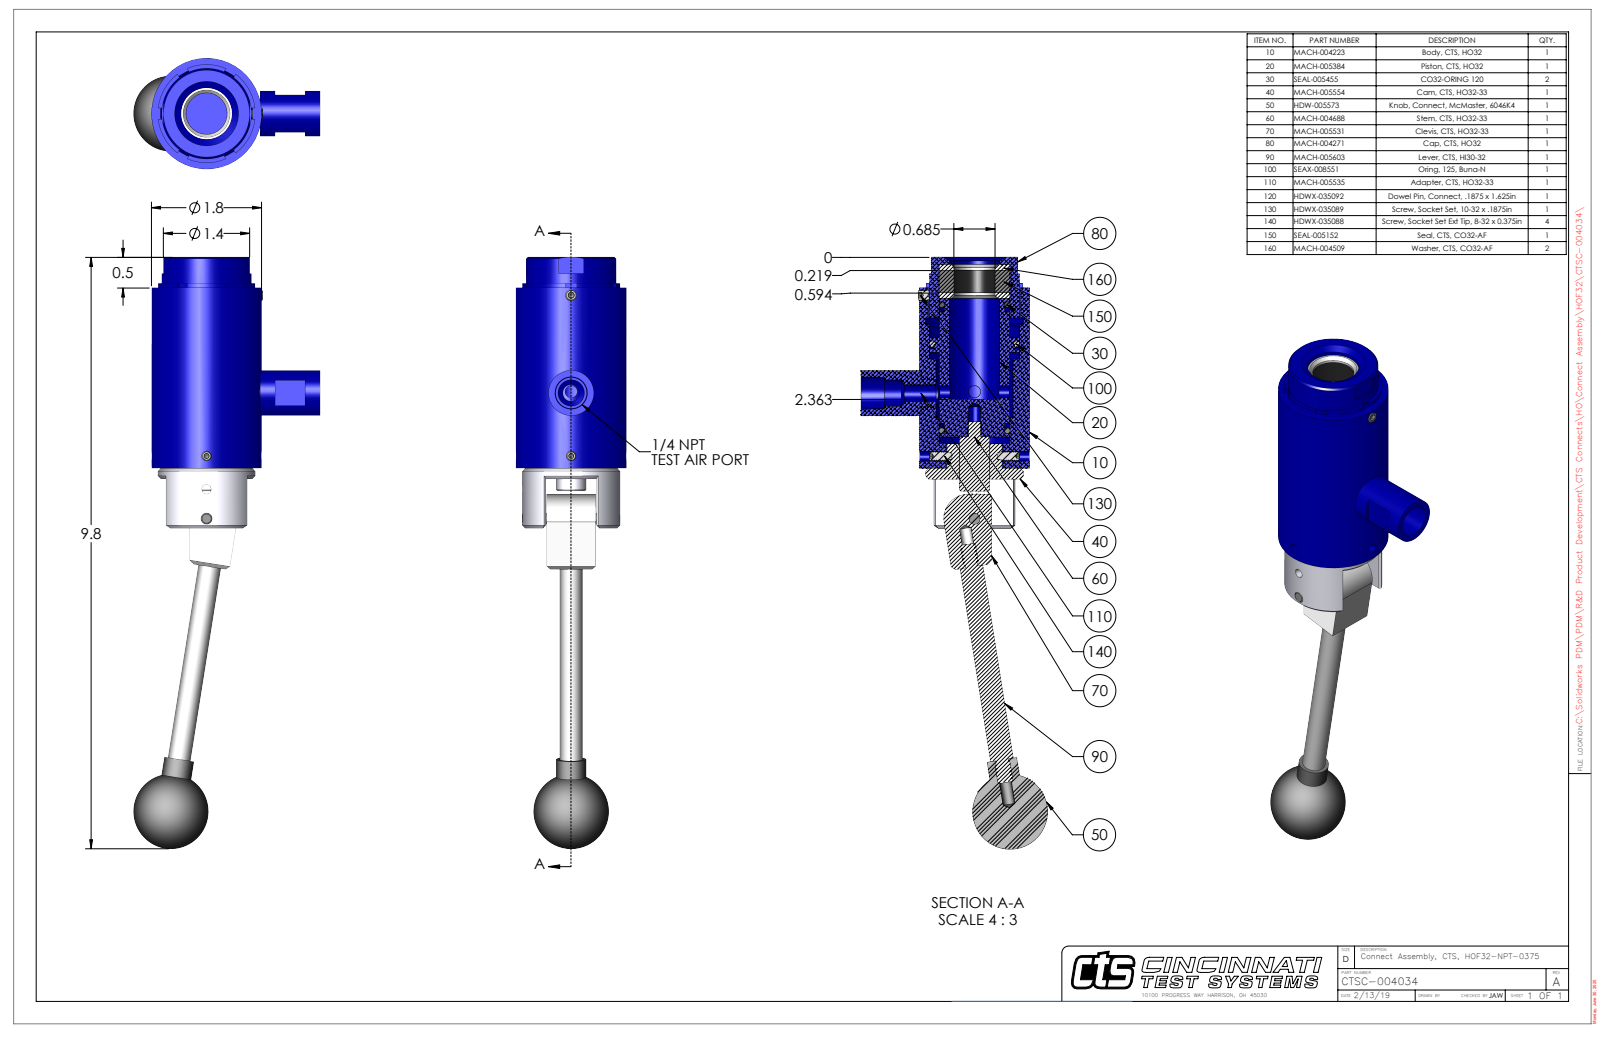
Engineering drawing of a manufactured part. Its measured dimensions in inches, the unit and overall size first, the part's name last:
Units: inches
Overall size (bounding box): 9.837 × 3.109 × 1.832
Round holes (diameter × count): ⌀0.201 ×3, ⌀0.159 ×2, ⌀0.094 ×1, ⌀0.189 ×1, ⌀0.19 ×1, ⌀0.203 ×1, ⌀0.203 ×1, ⌀0.281 ×1, ⌀0.438 ×1, ⌀0.453 ×1, ⌀0.516 ×1, ⌀0.527 ×1
Round bosses / shafts (diameter × count): ⌀0.75 ×2, ⌀0.5 ×2, ⌀0.164 ×2, ⌀0.109 ×2, ⌀1.832 ×1, ⌀1.625 ×1, ⌀1.495 ×1, ⌀1.172 ×1
Partial cylindrical surfaces — rounded edges, fillets, slot ends (radius × count): R0.228 ×1, R0.4 ×1, R0.77 ×1, R0.811 ×1, R0.839 ×1
Main face-to-face distances: 0.094, 0.469, 0.014, 0.826, 3, 0.375, 0.178, 3.094, 3.469, 0.84
Hole centre spacings: 0.022, 0.488, 1.128, 1.603, 1.622, 1.625, 2.11, 2.75
Volume: 10.8 in³ · Surface area: 79.86 in²
Bodies: 13 solids, 530 faces (178 planar, 216 cylindrical, 136 other)
Part name (STEP PRODUCT): CTSC-004034
STEP written by: SolidWorks 2023 (AUTOMOTIVE_DESIGN)
